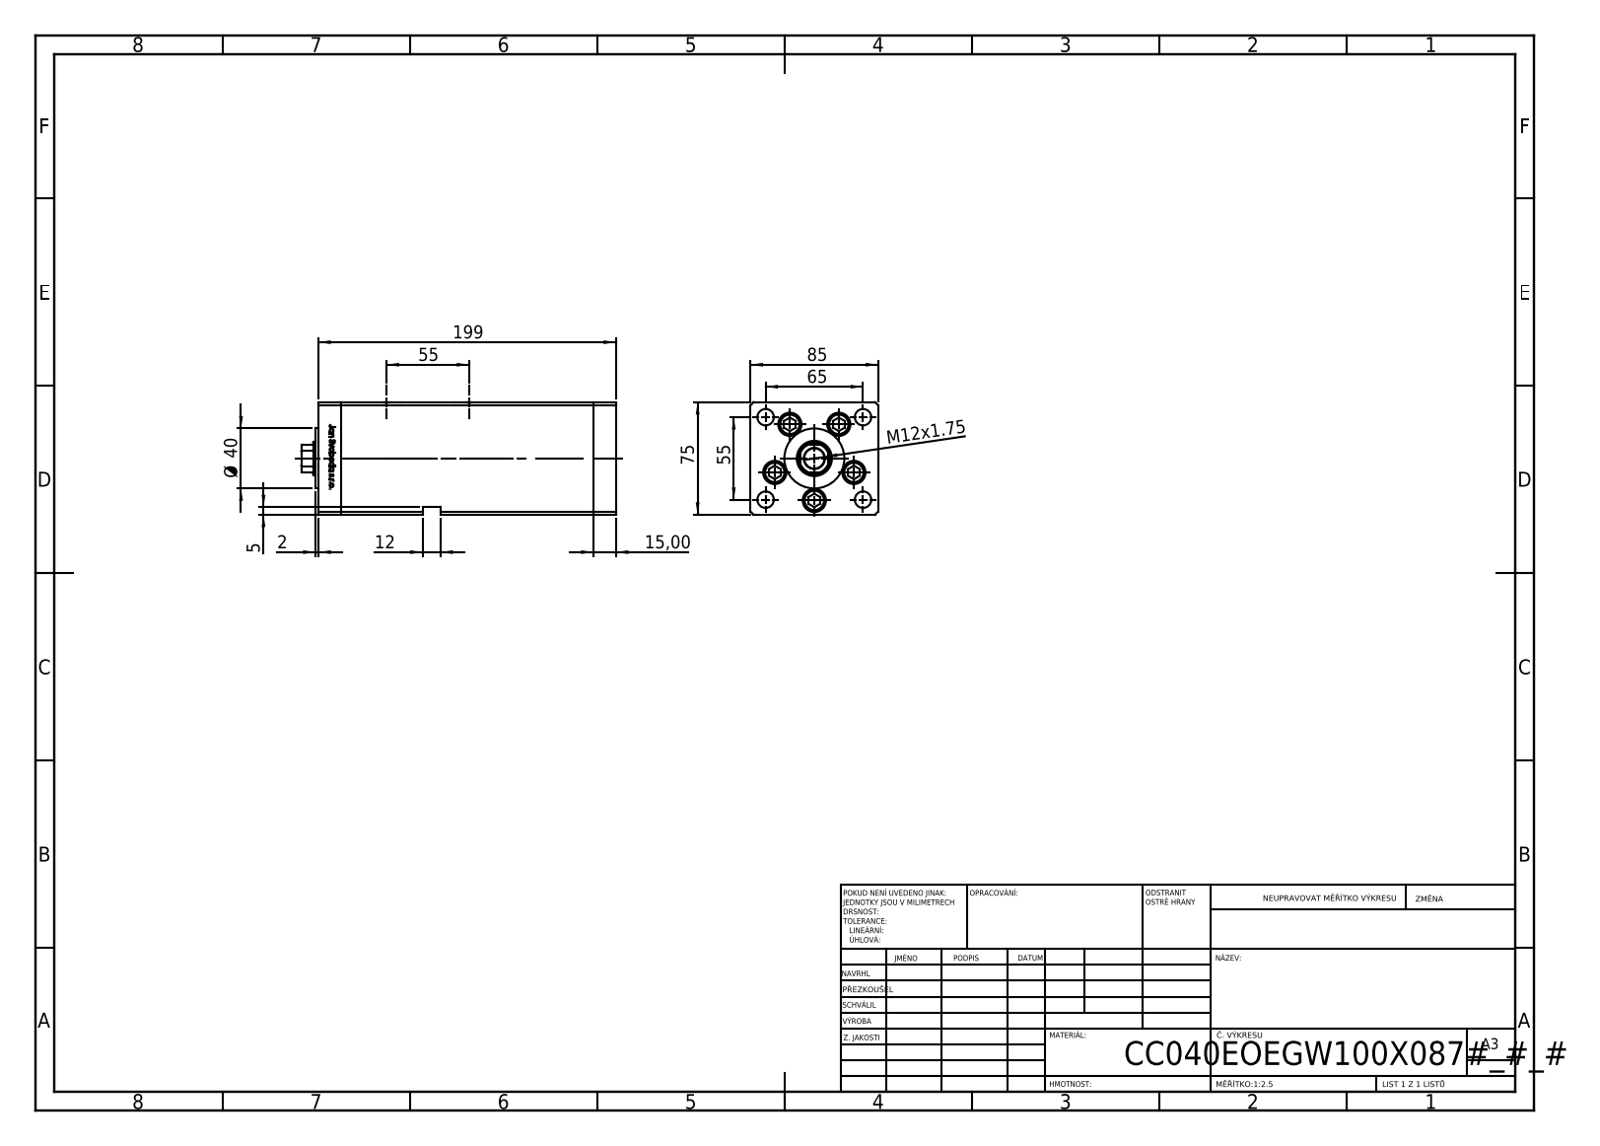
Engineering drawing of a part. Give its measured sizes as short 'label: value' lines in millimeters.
name: V220C_FRONT_E; V220C_VC_E; ALLEN BOLT; V220C BACK_E (+1 more)
written by: SolidWorks 2019 (CONFIG_CONTROL_DESIGN)
unit: mm
bodies: 14 solids, 1214 faces (475 planar, 165 cylindrical, 574 other)
size: 210 × 85 × 75
volume: 1 076 000 mm³; area: 182 851 mm²
holes: 9× ⌀11, 5× ⌀15.5, 4× ⌀10.5, 4× ⌀16.5, 2× ⌀2, 2× ⌀13.16, 1× ⌀13.5, 1× ⌀22, 1× ⌀23.5
bosses: 5× ⌀14.5, 5× ⌀8, 1× ⌀40
rounds: 2× R0.93, 1× R10.5
face distances: 85, 75, 15, 168.5, 183.5, 198.5, 34.25, 68.5, 10.5, 19.25
hole spacings: 28, 42.57, 55, 65, 85.15, 16.86, 19.17, 32.33
